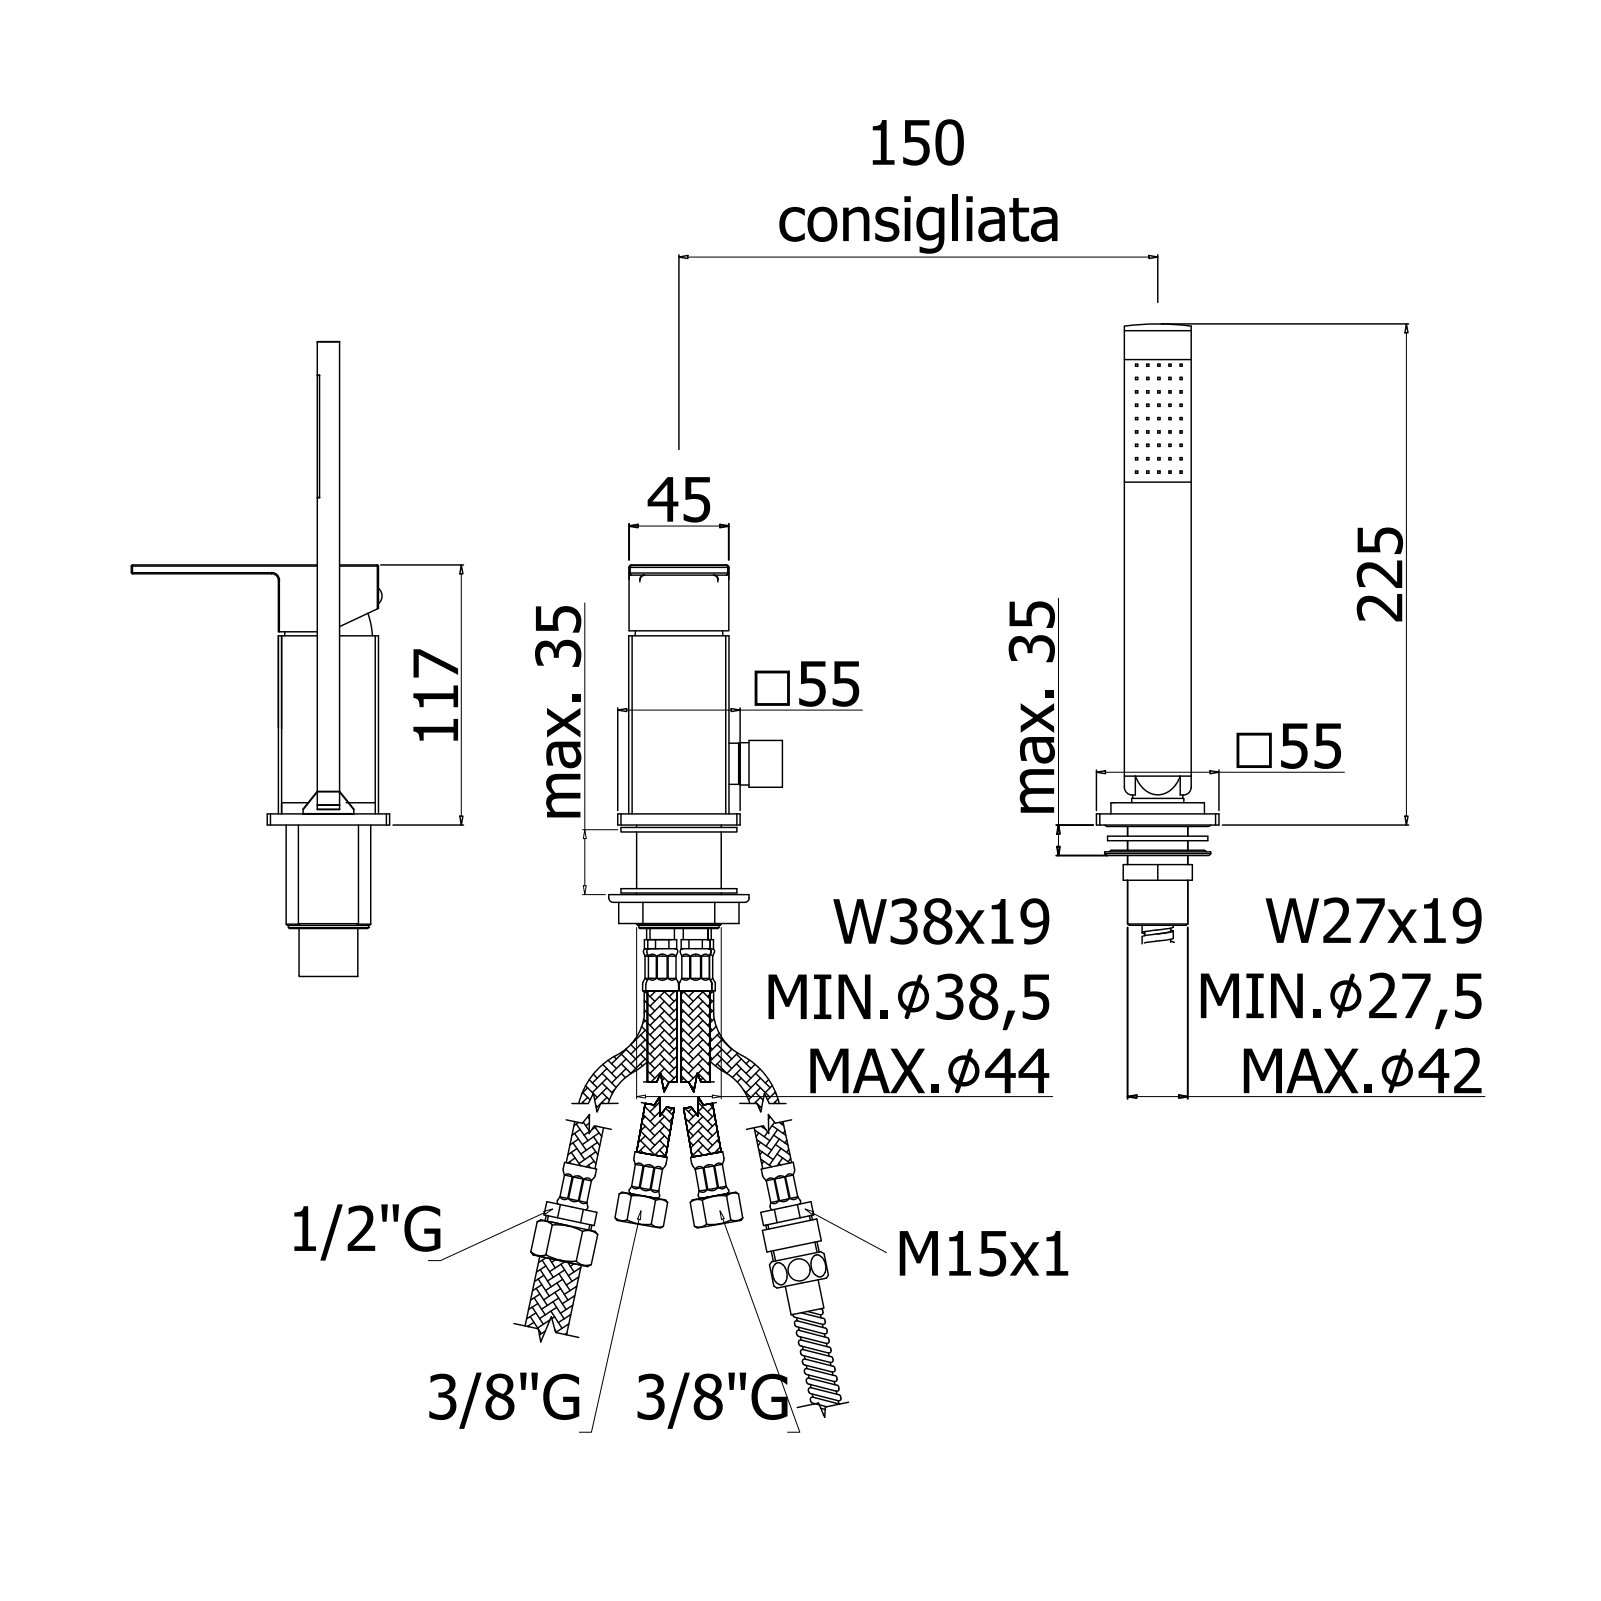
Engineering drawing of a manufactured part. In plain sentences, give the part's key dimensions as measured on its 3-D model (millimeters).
The part is named "EL041CR". Its 3-D file was written by "CREO PARAMETRIC BY PTC INC, 2020044 (CONFIG_CONTROL_DESIGN)". It is 3 solids with 321 faces: 104 planar, 130 cylindrical and 87 other. Overall it measures 223 by 205 by 116.58 millimeters. Its volume is 259 166 cubic millimeters and its surface area 83 637 square millimeters. Round holes: 7 of diameter 7, 2 of diameter 5, 1 of diameter 3.5, 1 of diameter 7.2, 1 of diameter 9, 1 of diameter 9.5, 1 of diameter 13, 1 of diameter 13.5, 1 of diameter 15.2, 1 of diameter 16, 1 of diameter 30.6, 1 of diameter 36. Round bosses or shafts: 1 of diameter 42.5, 1 of diameter 42, 1 of diameter 40, 1 of diameter 38, 1 of diameter 22.5, 1 of diameter 18.5, 1 of diameter 18, 1 of diameter 15. Partial cylindrical surfaces (rounded edges, fillets, slot ends): 22 of radius 1.5, 10 of radius 0.5, 4 of radius 2, 2 of radius 4, 2 of radius 300, 1 of radius 3, 1 of radius 8.5, 1 of radius 31.5. The main face-to-face distances are 45, 27.5, 17.5, 10, 5, 30, 142.5, 187.5, 157.5, 112.5. The hole center spacings are 3, 8.6, 10.63, 13.45, 14, 14.32, 15.13, 18.11.
